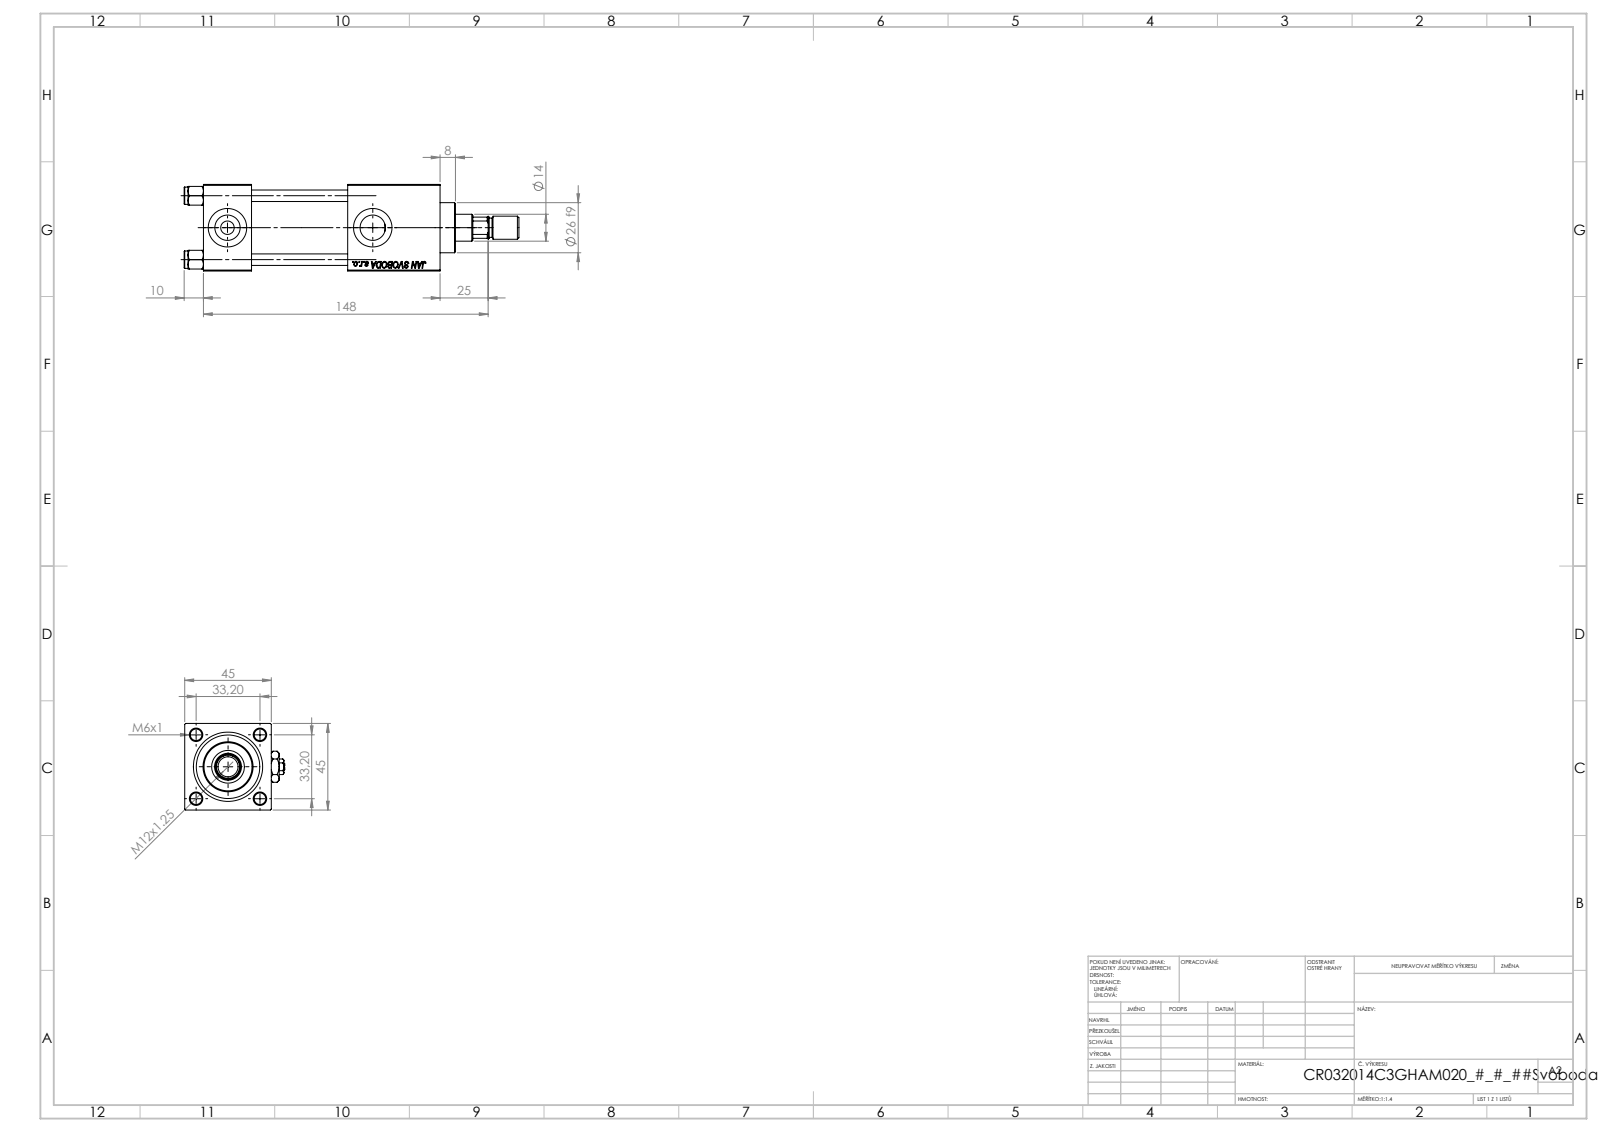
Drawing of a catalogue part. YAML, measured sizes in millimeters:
part_name: "V215CR_VCP_C; V215CR_C_TYCINKA; V215CR_C_Body; Zatka_pro_OIL_PORT (+3 more)"
step_written_by: "SolidWorks 2019 (CONFIG_CONTROL_DESIGN)"
units: millimeters
bodies: {solids: 14, faces: 1262, planar: 576, cylindrical: 102, other: 584}
overall_size: [174, 52, 45]
volume: 194069
surface_area: 69775
round_holes:
  - {diameter: 6, count: 4}
  - {diameter: 7, count: 2}
  - {diameter: 13.16, count: 2}
  - {diameter: 20, count: 2}
  - {diameter: 6.5, count: 1}
  - {diameter: 14, count: 1}
  - {diameter: 17, count: 1}
  - {diameter: 24, count: 1}
  - {diameter: 32, count: 1}
  - {diameter: 33, count: 1}
round_bosses_or_shafts:
  - {diameter: 9, count: 4}
  - {diameter: 38, count: 1}
  - {diameter: 26, count: 1}
  - {diameter: 12, count: 1}
  - {diameter: 10, count: 1}
partial_cylinders:
  - {radius: 6.5, count: 1}
face_to_face_distances: [45, 25, 123, 98, 50, 75, 48, 94.3, 69.3, 19.3]
hole_center_spacings: [23.48, 33.2, 46.95, 75.5]
